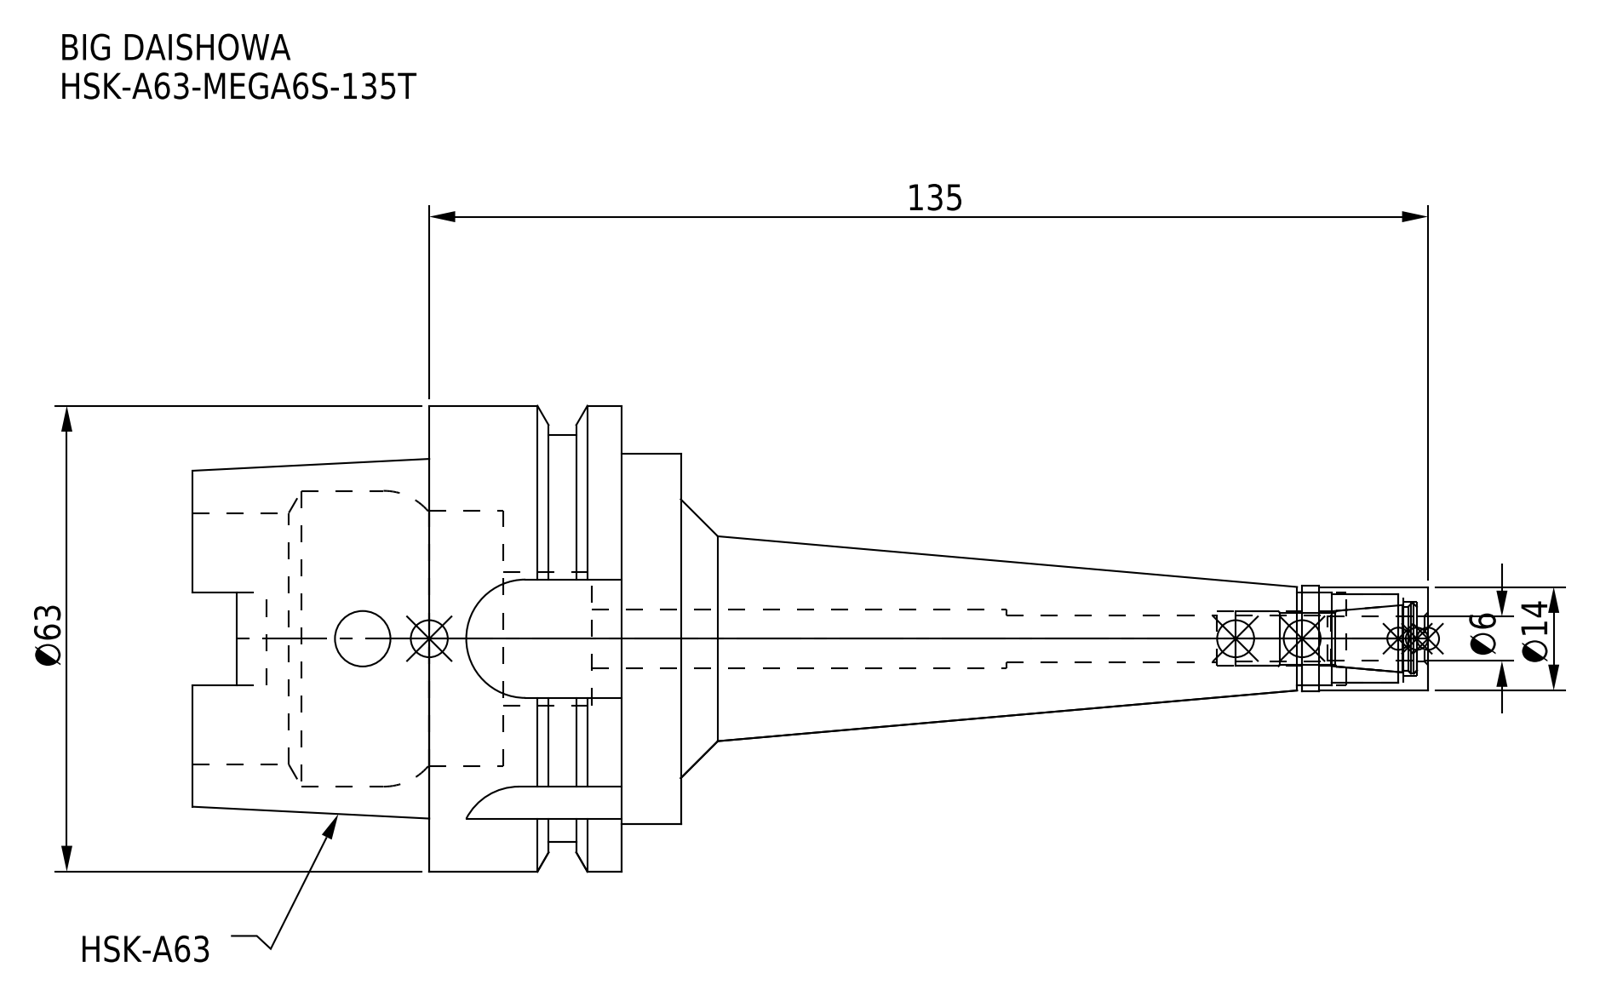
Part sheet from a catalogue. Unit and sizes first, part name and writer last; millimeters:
Units: millimetres
Overall size (bounding box): 167 × 63 × 63
Round holes (diameter × count): ⌀6.1 ×1, ⌀6.4 ×1, ⌀7.4 ×1, ⌀7.5 ×1, ⌀8 ×1, ⌀10 ×1, ⌀12 ×1, ⌀12.5 ×1, ⌀18 ×1, ⌀34 ×1, ⌀34.5 ×1, ⌀40 ×1
Round bosses / shafts (diameter × count): ⌀63 ×1, ⌀55 ×1, ⌀50 ×1, ⌀14.3 ×1, ⌀14 ×1
Partial cylindrical surfaces — rounded edges, fillets, slot ends (radius × count): R2.88 ×4, R8 ×4
Main face-to-face distances: 26, 8, 34, 24.05, 16.05, 9.95, 66, 58, 41.95, 32
Volume: 127 054 mm³ · Surface area: 33 121 mm²
Bodies: 2 solids, 122 faces (47 planar, 53 cylindrical, 22 other)
Part name (STEP PRODUCT): DXF_TEMP_ASSY_ASM_4_ASM.stp; HSK-A63-MEGA6S-135T_1.stp; MGN6S_1.stp; HSK-A63-MEGA6S-135T (+3 more)
STEP written by: SolidWorks 2019 (CONFIG_CONTROL_DESIGN)
